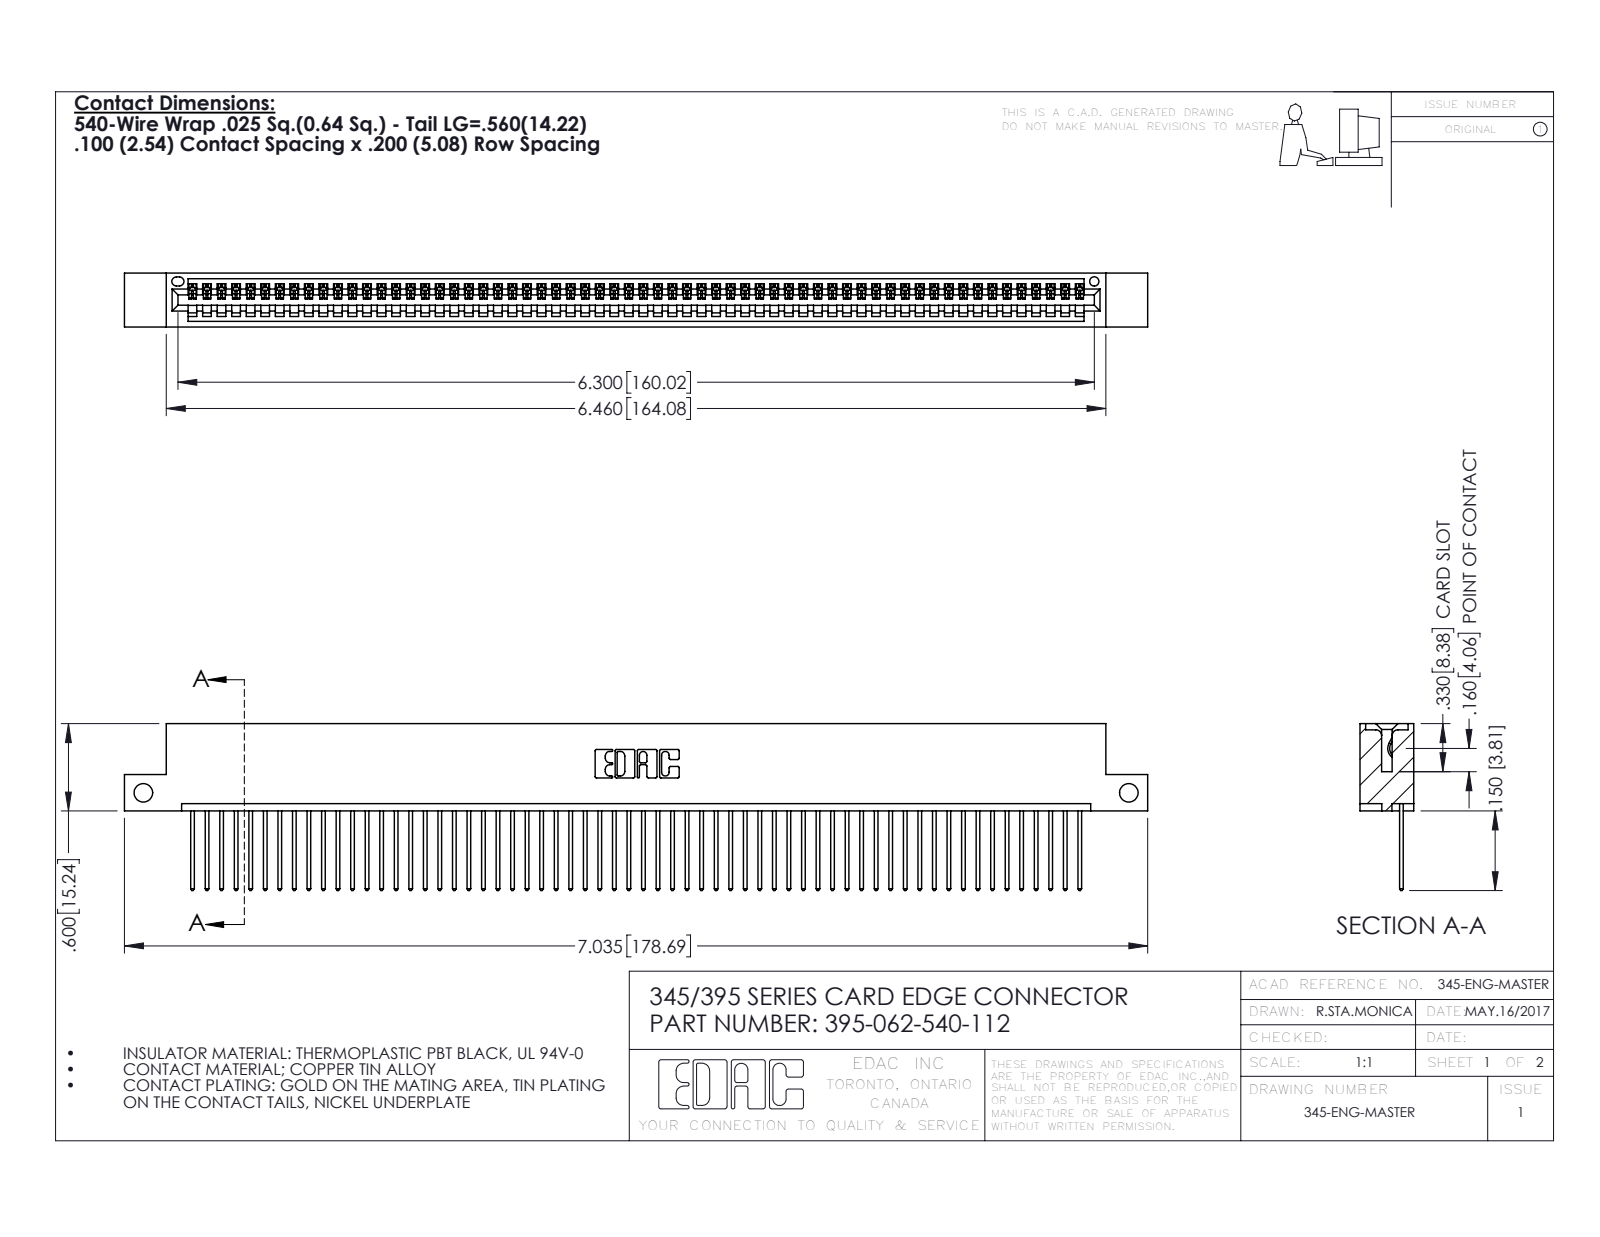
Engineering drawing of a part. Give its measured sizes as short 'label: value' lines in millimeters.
name: 345-292-001_345-293-140; 345 Part_Flush Mounting Lugs - Side Mount; 395-062-540-112
written by: SolidWorks 2016 (CONFIG_CONTROL_DESIGN)
unit: mm
bodies: 63 solids, 3722 faces (2560 planar, 1162 cylindrical, 0 other)
size: 178.7 × 29.1 × 9.4
volume: 17 120 mm³; area: 23 500 mm²
holes: 2× ⌀3.3, 1× ⌀1.6
rounds: 124× R0.2, 124× R0.3, 22× R0.3, 6× R0.2, 6× R0.8, 3× R0.7, 2× R0.8, 2× R1
face distances: 1.8, 7.6, 9.4, 2.5, 6.9, 0.6, 5.1, 5.7, 3.8, 1.8
hole spacings: 172.1
